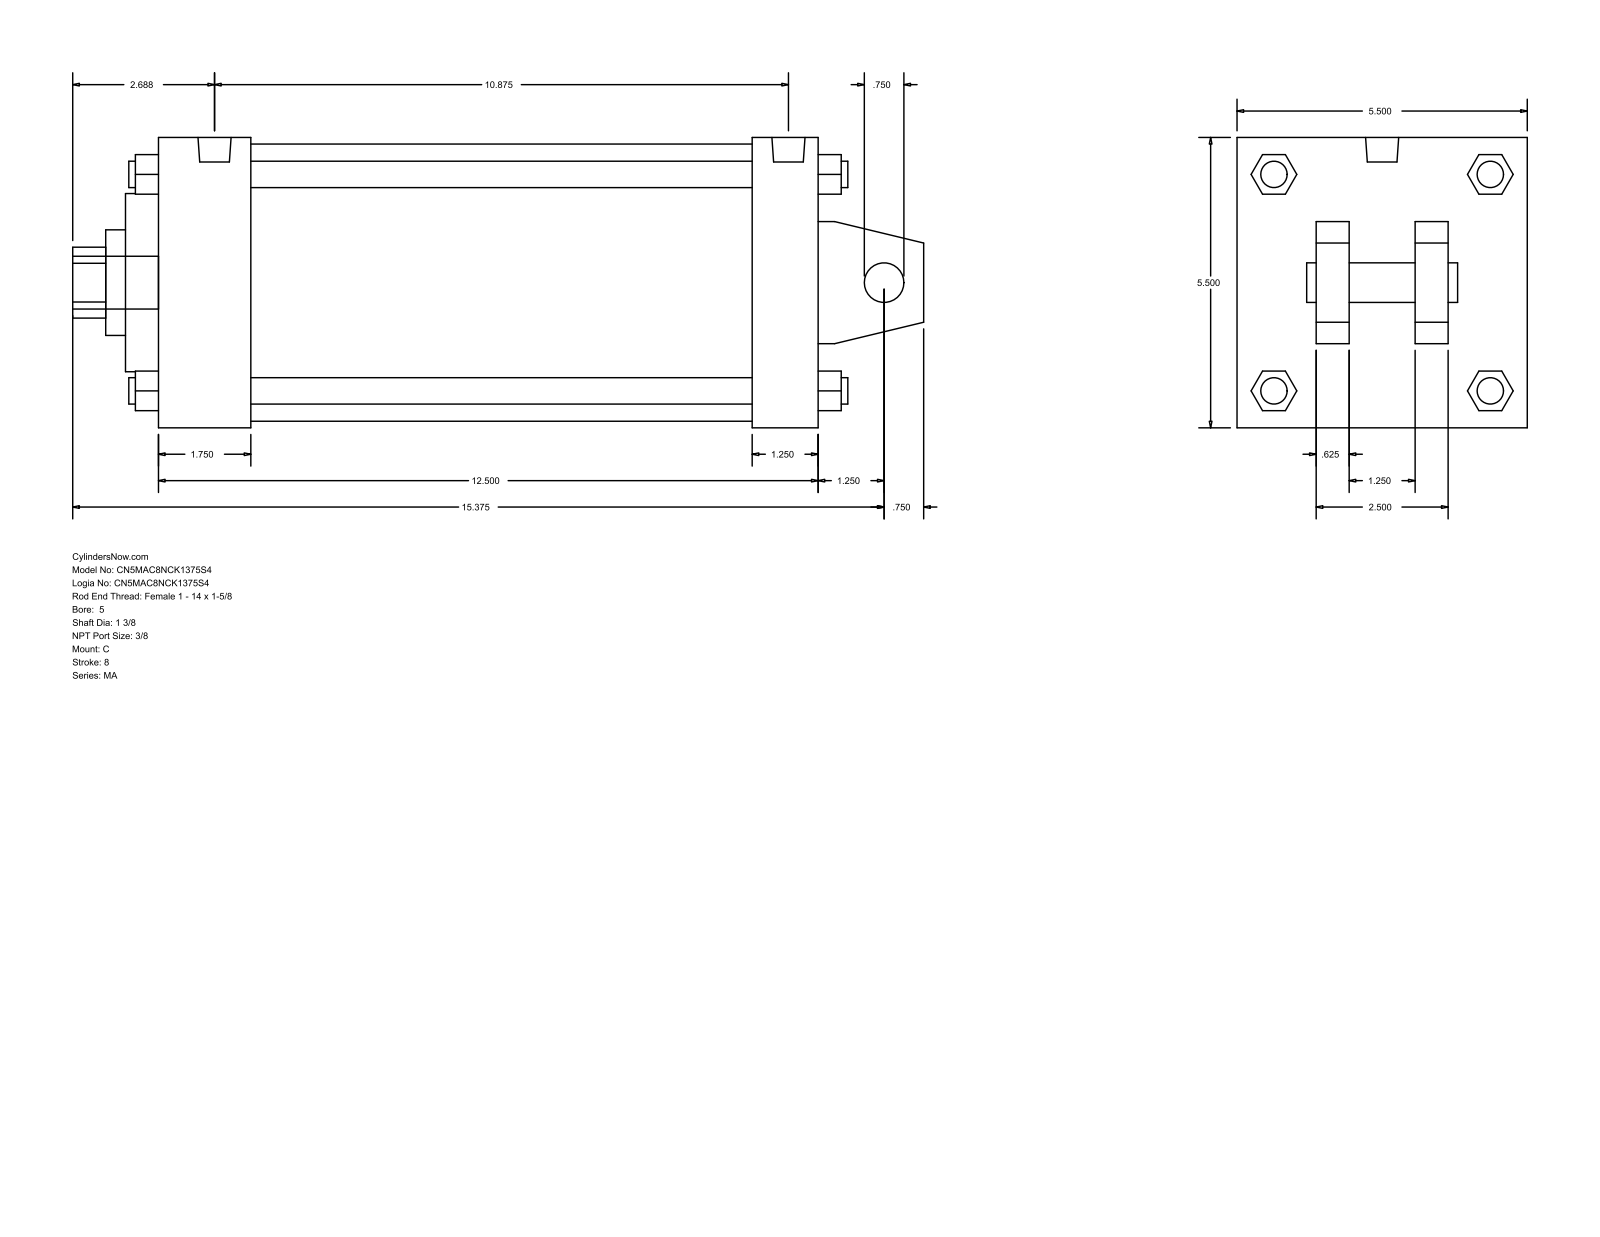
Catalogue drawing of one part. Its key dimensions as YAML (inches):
part_name: "MA_C__0500_1.375"
step_written_by: "GSSL Pune (CONFIG_CONTROL_DESIGN)"
units: inches
bodies: {solids: 0, faces: 141, planar: 109, cylindrical: 32, other: 0}
overall_size: [16.125, 5.5, 5.5]
round_holes:
  - {diameter: 0.75, count: 1}
  - {diameter: 1.375, count: 1}
  - {diameter: 2, count: 1}
  - {diameter: 3.375, count: 1}
  - {diameter: 5.25, count: 1}
round_bosses_or_shafts:
  - {diameter: 0.5, count: 4}
  - {diameter: 0.437, count: 4}
  - {diameter: 0.627, count: 2}
  - {diameter: 1, count: 1}
partial_cylinders:
  - {radius: 0.672, count: 1}
face_to_face_distances: [5.5, 12.5, 0.625, 11.25, 1.25, 1.75, 9.5, 10.75, 1.5, 4]
